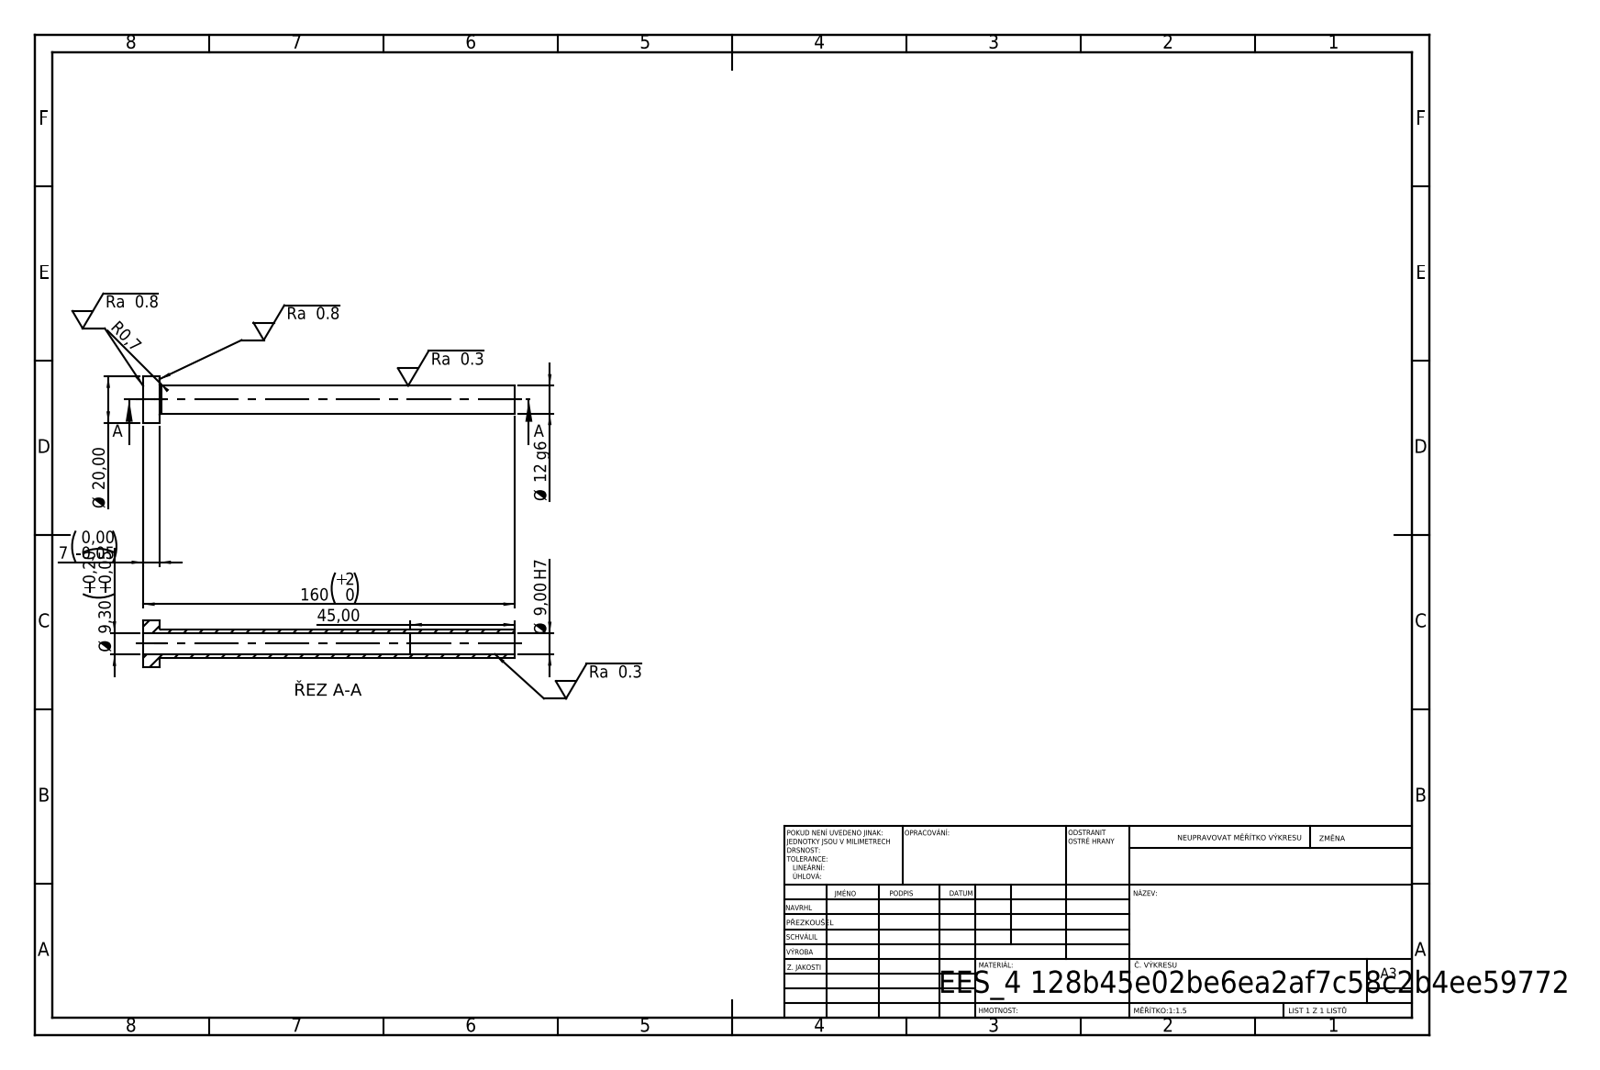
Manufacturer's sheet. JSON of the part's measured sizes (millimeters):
{"step_written_by": "SolidWorks 2019 (CONFIG_CONTROL_DESIGN)", "units": "millimeters", "bodies": {"solids": 1, "faces": 14, "planar": 4, "cylindrical": 8, "other": 2}, "overall_size": [160, 20, 20], "volume_mm3": 8832, "surface_area_mm2": 11330, "round_holes": [[9, 1], [9.3, 1]], "round_bosses_or_shafts": [[20, 1], [12, 1]], "face_to_face_distances": [7, 160, 153, 115, 108, 45]}
